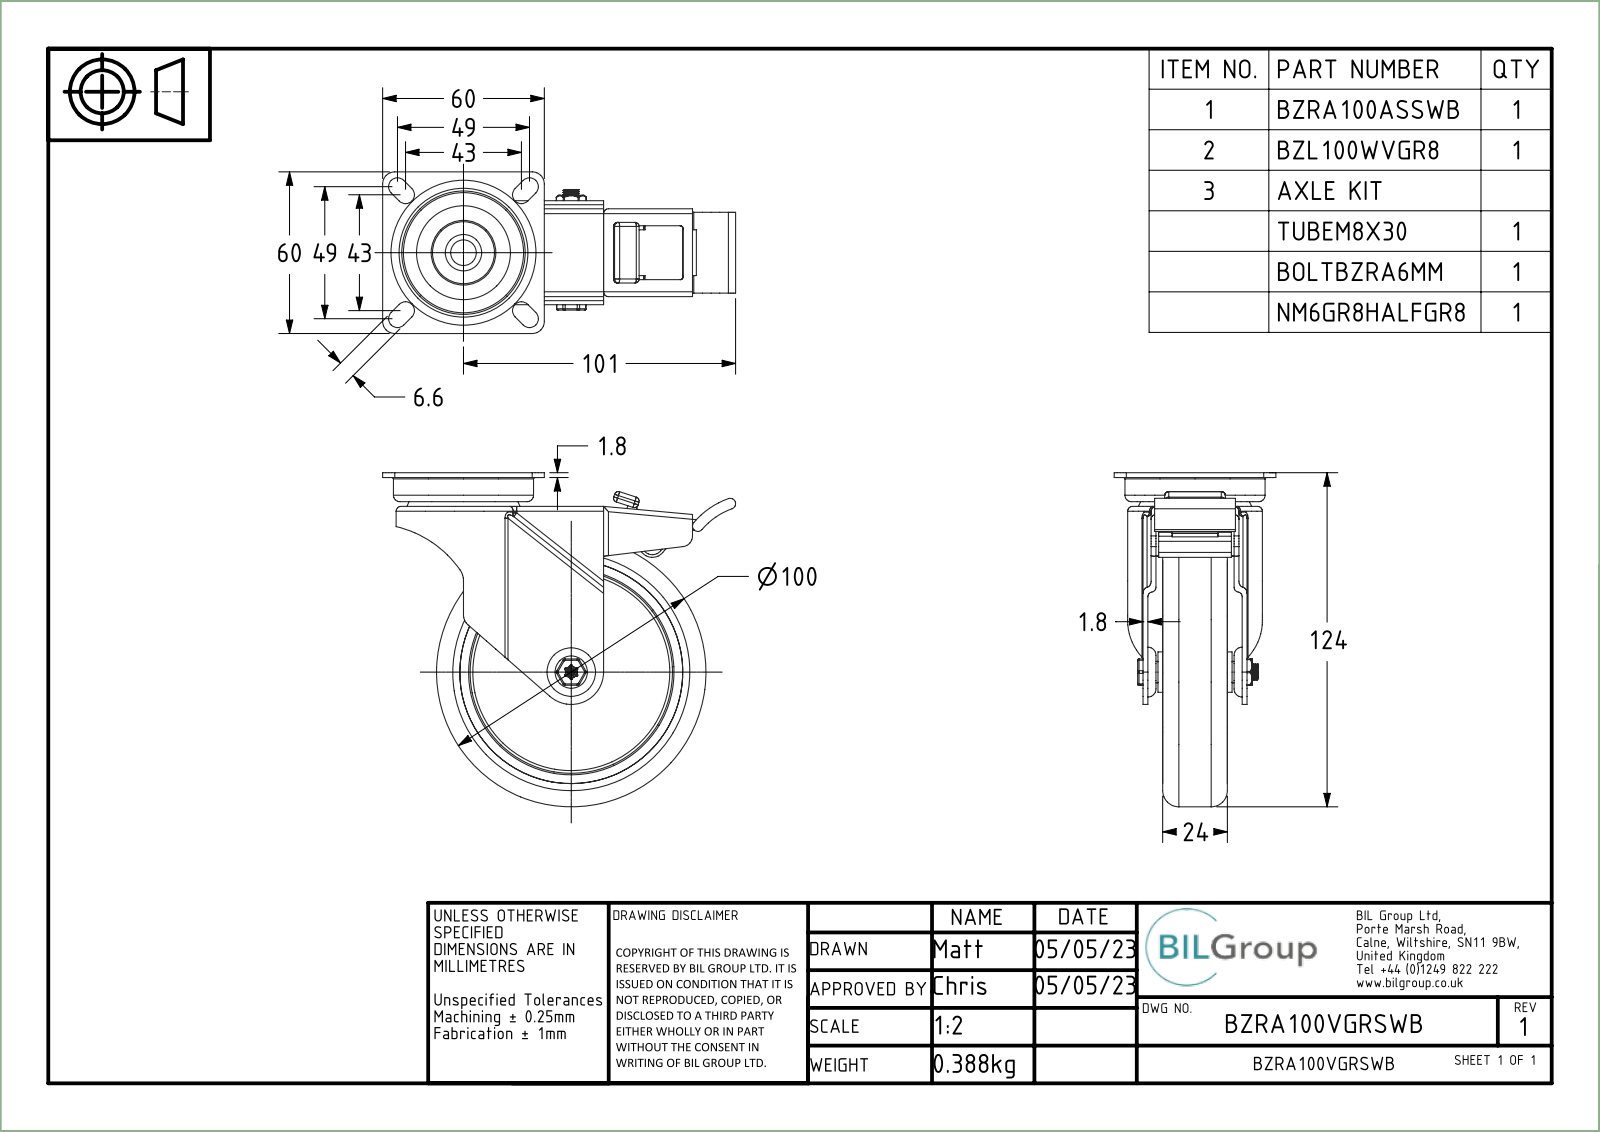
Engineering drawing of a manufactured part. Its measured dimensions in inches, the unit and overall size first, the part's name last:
Units: inches
Overall size (bounding box): 5.157 × 4.882 × 2.362
Round holes (diameter × count): ⌀0.236 ×1, ⌀0.248 ×1, ⌀0.252 ×1, ⌀0.323 ×1, ⌀0.327 ×1, ⌀0.374 ×1, ⌀1.181 ×1, ⌀1.652 ×1, ⌀1.882 ×1, ⌀3.258 ×1
Round bosses / shafts (diameter × count): ⌀0.591 ×2, ⌀3.937 ×1, ⌀2.047 ×1, ⌀1.535 ×1, ⌀0.531 ×1, ⌀0.315 ×1, ⌀0.313 ×1, ⌀0.197 ×1
Partial cylindrical surfaces — rounded edges, fillets, slot ends (radius × count): R0.071 ×27, R0.039 ×22, R0.02 ×13, R0.059 ×12, R0.13 ×8, R0.016 ×6, R0.035 ×4, R0.079 ×4
Main face-to-face distances: 0.071, 1.331, 0.236, 0.118, 0.189, 0.098, 0.591, 1.232, 0.453, 0.354
Volume: 9.563 in³ · Surface area: 139.6 in²
Bodies: 10 solids, 683 faces (229 planar, 284 cylindrical, 170 other)
Part name (STEP PRODUCT): BZRA100ASSWB; ZINC PLATED PRESSED STEEL TOP PLATE; ZINC PLATED PRESSED STEEL FORKS; ZINC PLATED PRESSED STEEL BRAKE (+8 more)
STEP written by: Spatial InterOp 3D (CONFIG_CONTROL_DESIGN)
